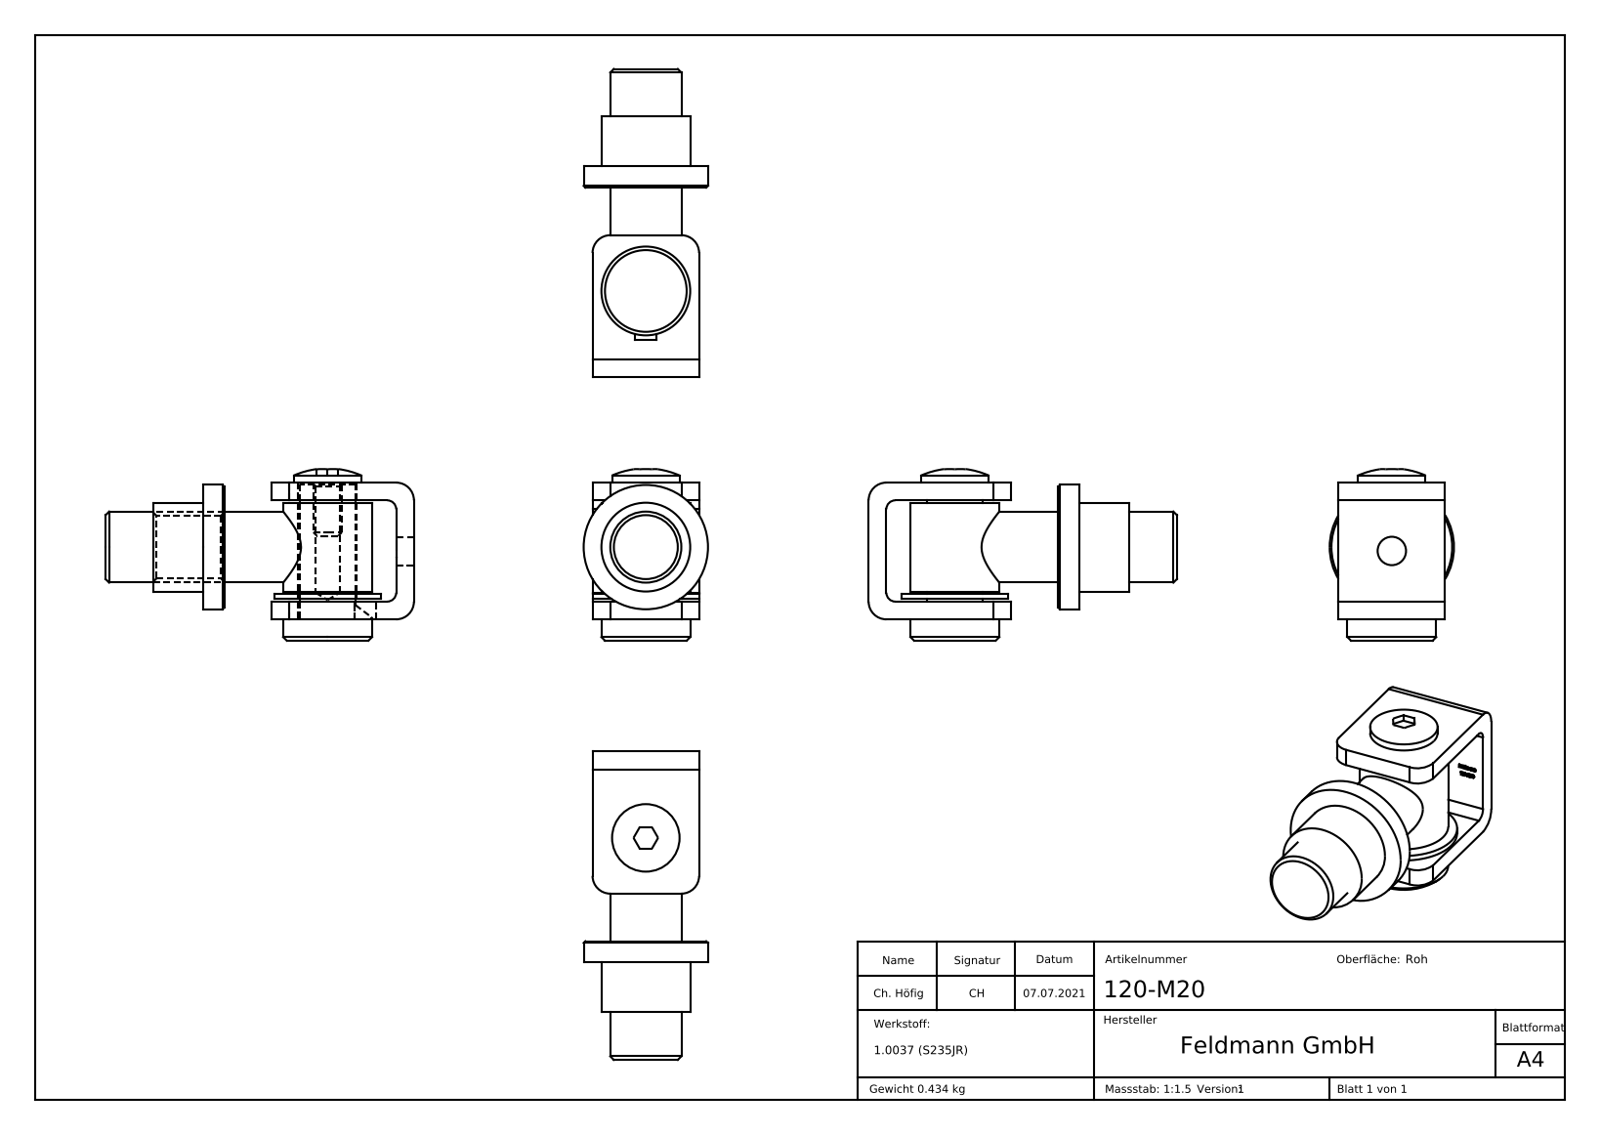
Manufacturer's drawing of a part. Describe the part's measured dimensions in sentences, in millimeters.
The part is named "Torband Teil4_120-M20 Teil4; Torband Teil1; Torband Teil5; Torband Teil6_120-M20 Teil6 (+8 more)". Its 3-D file was written by "SolidWorks 2018 (CONFIG_CONTROL_DESIGN)". It is 6 solids with 328 faces: 170 planar, 40 cylindrical and 118 other. Overall it measures 86.8 by 48.31 by 35 millimeters. Its volume is 55 600 cubic millimeters and its surface area 24 787 square millimeters. Round holes: 1 of diameter 6.8, 1 of diameter 8, 1 of diameter 16.5, 1 of diameter 17.5. Round bosses or shafts: 2 of diameter 25, 1 of diameter 35, 1 of diameter 30, 1 of diameter 20, 1 of diameter 19, 1 of diameter 15.7, 1 of diameter 8. Partial cylindrical surfaces (rounded edges, fillets, slot ends): 4 of radius 5, 2 of radius 2.5. The main face-to-face distances are 5, 33.5, 38.5, 6, 5.67, 32.83, 0.67, 27.83, 28.5, 53.4. The hole center spacings are 1.08.
